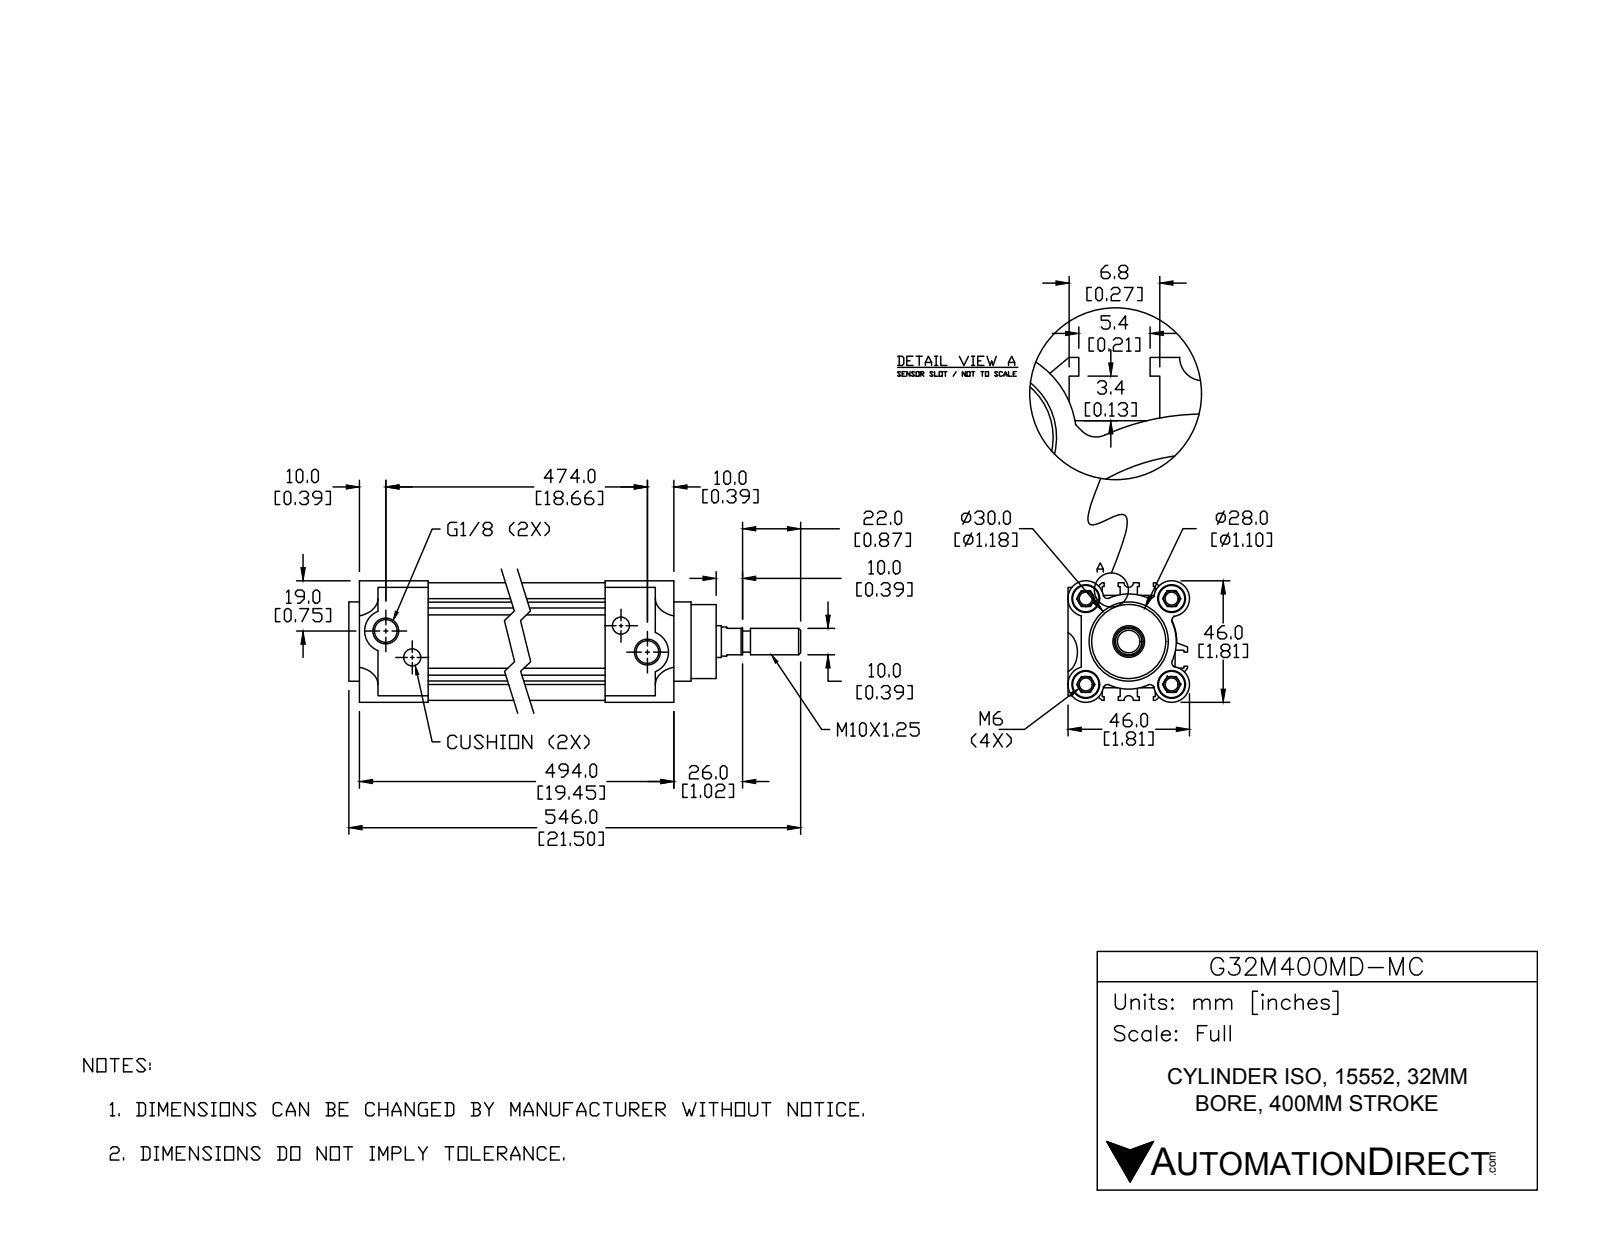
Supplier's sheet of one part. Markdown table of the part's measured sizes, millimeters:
| quantity | value |
| --- | --- |
| part name | 32121-HR; 32-HL; 32-400-73.5-B; 32121400-R (+1 more) |
| STEP written by | SolidWorks 2015 (CONFIG_CONTROL_DESIGN) |
| units | millimeters |
| bodies | 4 solids, 411 faces (229 planar, 138 cylindrical, 44 other) |
| overall size | 546 × 46 × 46 |
| volume | 566 000 mm³ |
| surface area | 214 400 mm² |
| round holes (diameter × count) | 4.9 × 4, 10.5 × 4, 6.5 × 2, 8.6 × 2, 12 × 1 |
| round bosses / shafts (diameter × count) | 10 × 5, 32 × 1, 30 × 1, 28 × 1, 11 × 1, 8 × 1 |
| partial cylindrical surfaces (radius × count) | 0.1 × 12, 1.5 × 6, 6 × 4, 6.8 × 4, 1.8 × 2, 8 × 2, 18 × 1, 18.2 × 1 |
| main face-to-face distances | 39.8, 4.7, 6.8, 25.5, 19, 12.2, 32.3, 35, 44.5, 13.3 |
| hole center spacings | 23, 32.5, 14.1, 45.9, 464, 454.2, 474.1 |
